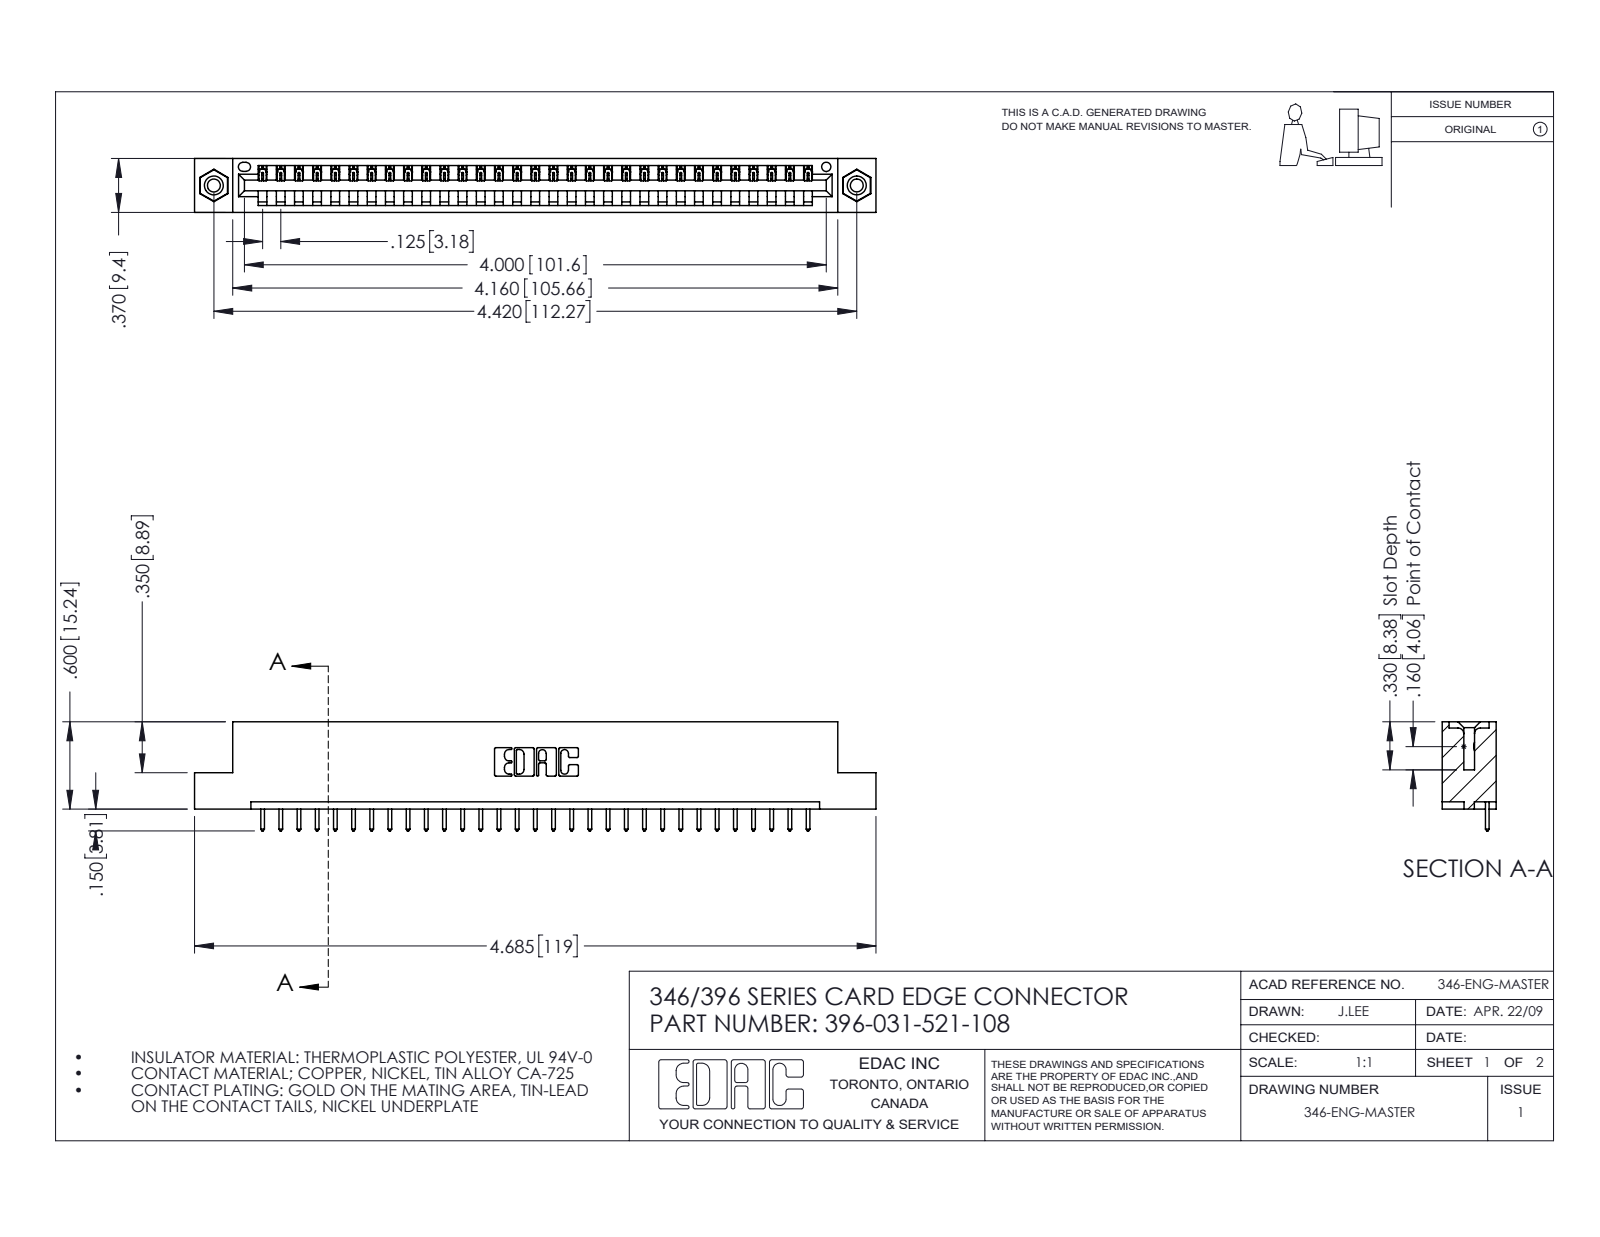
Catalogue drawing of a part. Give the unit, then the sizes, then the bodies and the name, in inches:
Units: inches
Overall size (bounding box): 4.685 × 0.75 × 0.37
Round holes (diameter × count): ⌀0.089 ×2, ⌀0.125 ×2, ⌀0.156 ×2, ⌀0.064 ×1
Round bosses / shafts (diameter × count): ⌀0.155 ×2
Partial cylindrical surfaces — rounded edges, fillets, slot ends (radius × count): R0.006 ×62, R0.01 ×62, R0.01 ×22, R0.007 ×6, R0.031 ×6, R0.026 ×3, R0.031 ×2, R0.04 ×2
Main face-to-face distances: 0.048, 0.322, 0.37, 0.25, 0.072, 0.298, 0.025, 0.148, 0.222, 0.1
Hole centre spacings: 0.246, 4.212, 4.42
Volume: 0.685 in³ · Surface area: 21.04 in²
Bodies: 34 solids, 1980 faces (1348 planar, 616 cylindrical, 16 other)
Part name (STEP PRODUCT): 396-031-521-108; 346 Part_Flush Mounting Lugs - 0.156 Dia-TI; 345-250-001_345-250-003-102; 345-292-001_345-293-121
STEP written by: SolidWorks 2016 (CONFIG_CONTROL_DESIGN)
